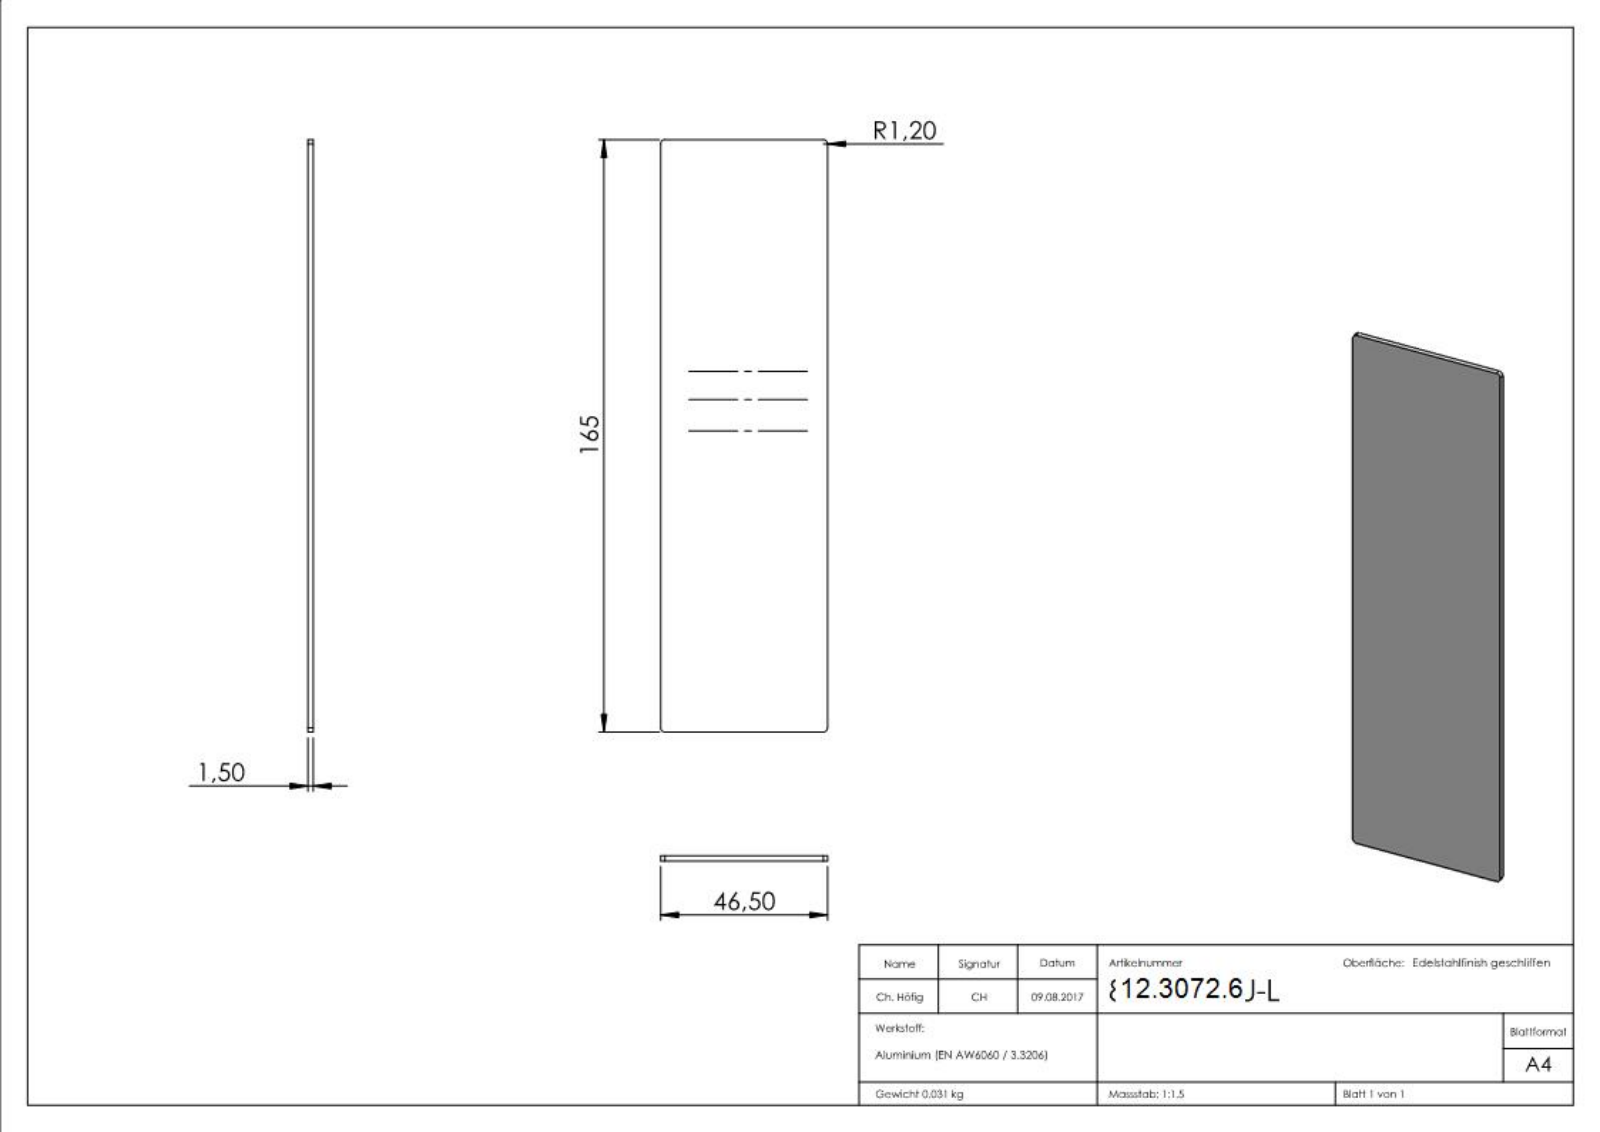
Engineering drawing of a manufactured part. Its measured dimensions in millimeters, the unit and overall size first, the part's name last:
Units: millimetres
Overall size (bounding box): 165 × 46.5 × 1.5
Partial cylindrical surfaces — rounded edges, fillets, slot ends (radius × count): R1.2 ×4
Main face-to-face distances: 1.5, 46.5, 165, 1.4, 1.19, 5.62, 2.98, 4.23, 2.64, 8.89
Volume: 11 506 mm³ · Surface area: 15 984 mm²
Bodies: 1 solid, 249 faces (139 planar, 4 cylindrical, 106 other)
Part name (STEP PRODUCT): 80556-ALU-L
STEP written by: SolidWorks 2015 (CONFIG_CONTROL_DESIGN)
